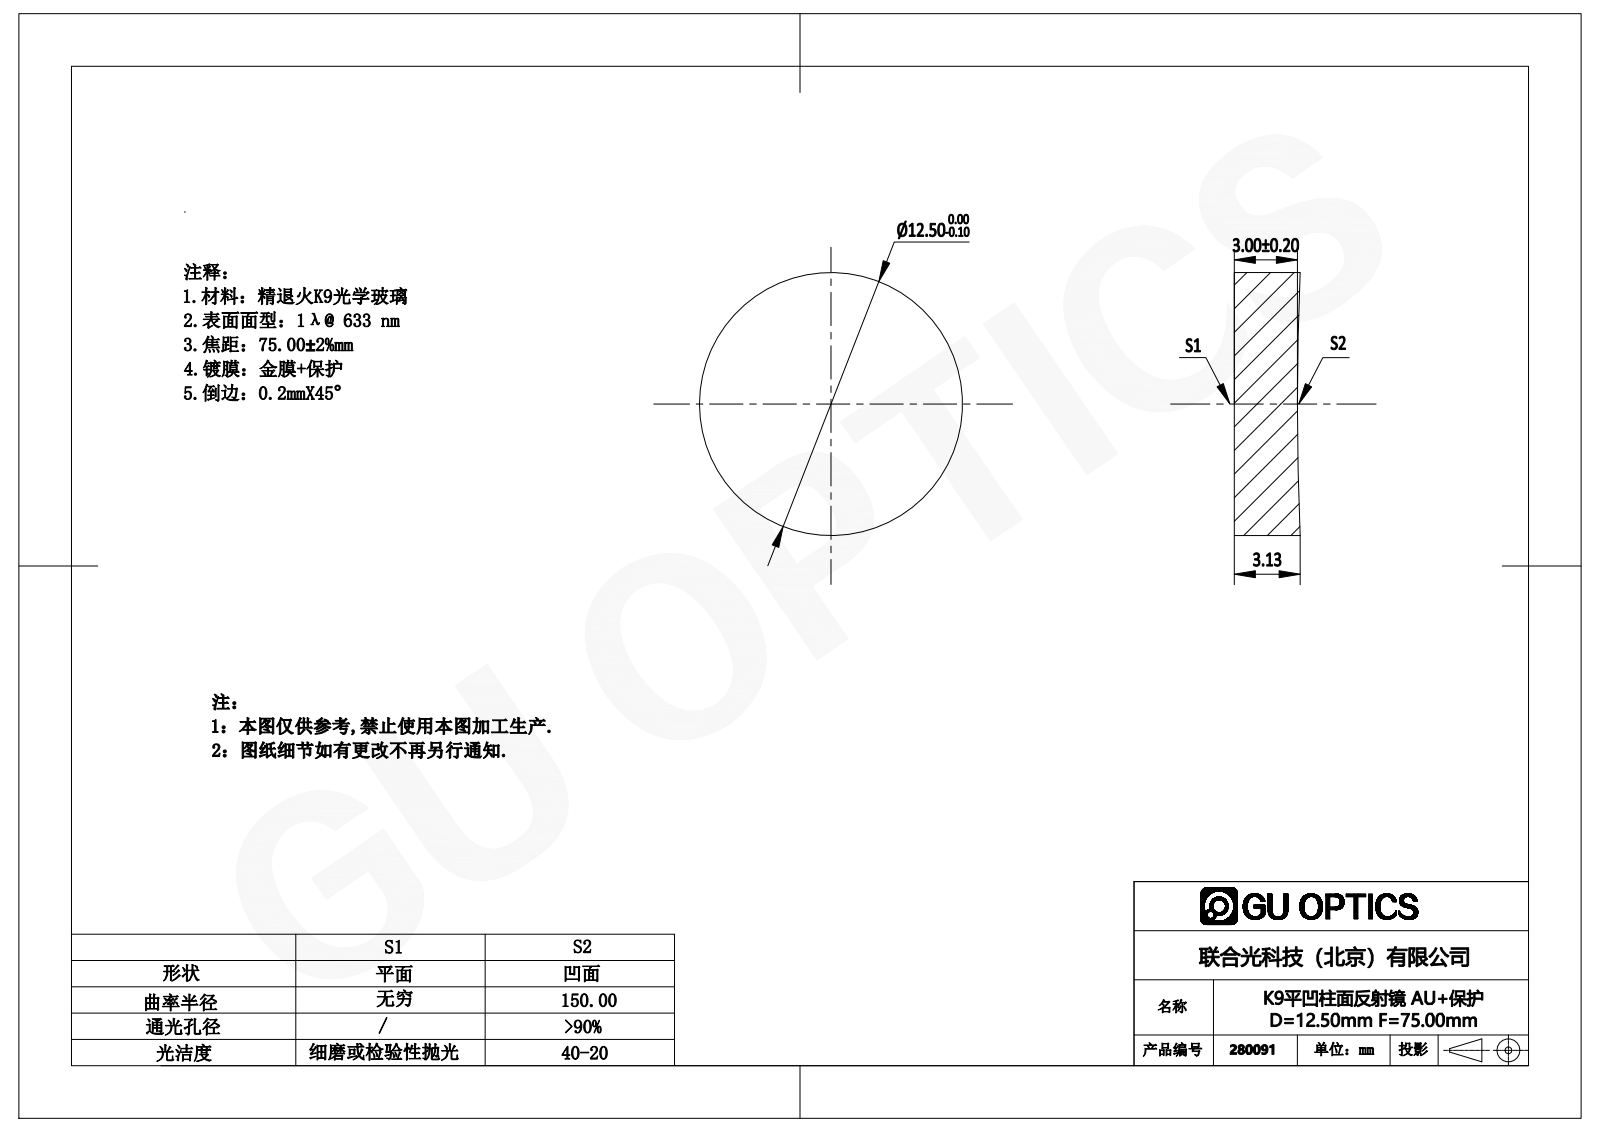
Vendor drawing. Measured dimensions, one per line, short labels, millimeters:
name: 280003
written by: SolidWorks 2020 (CONFIG_CONTROL_DESIGN)
unit: mm
bodies: 1 solid, 3 faces (1 planar, 2 cylindrical, 0 other)
size: 12.5 × 12.5 × 3.13
volume: 372 mm³; area: 366 mm²
bosses: 1× ⌀12.5
rounds: 1× R150
